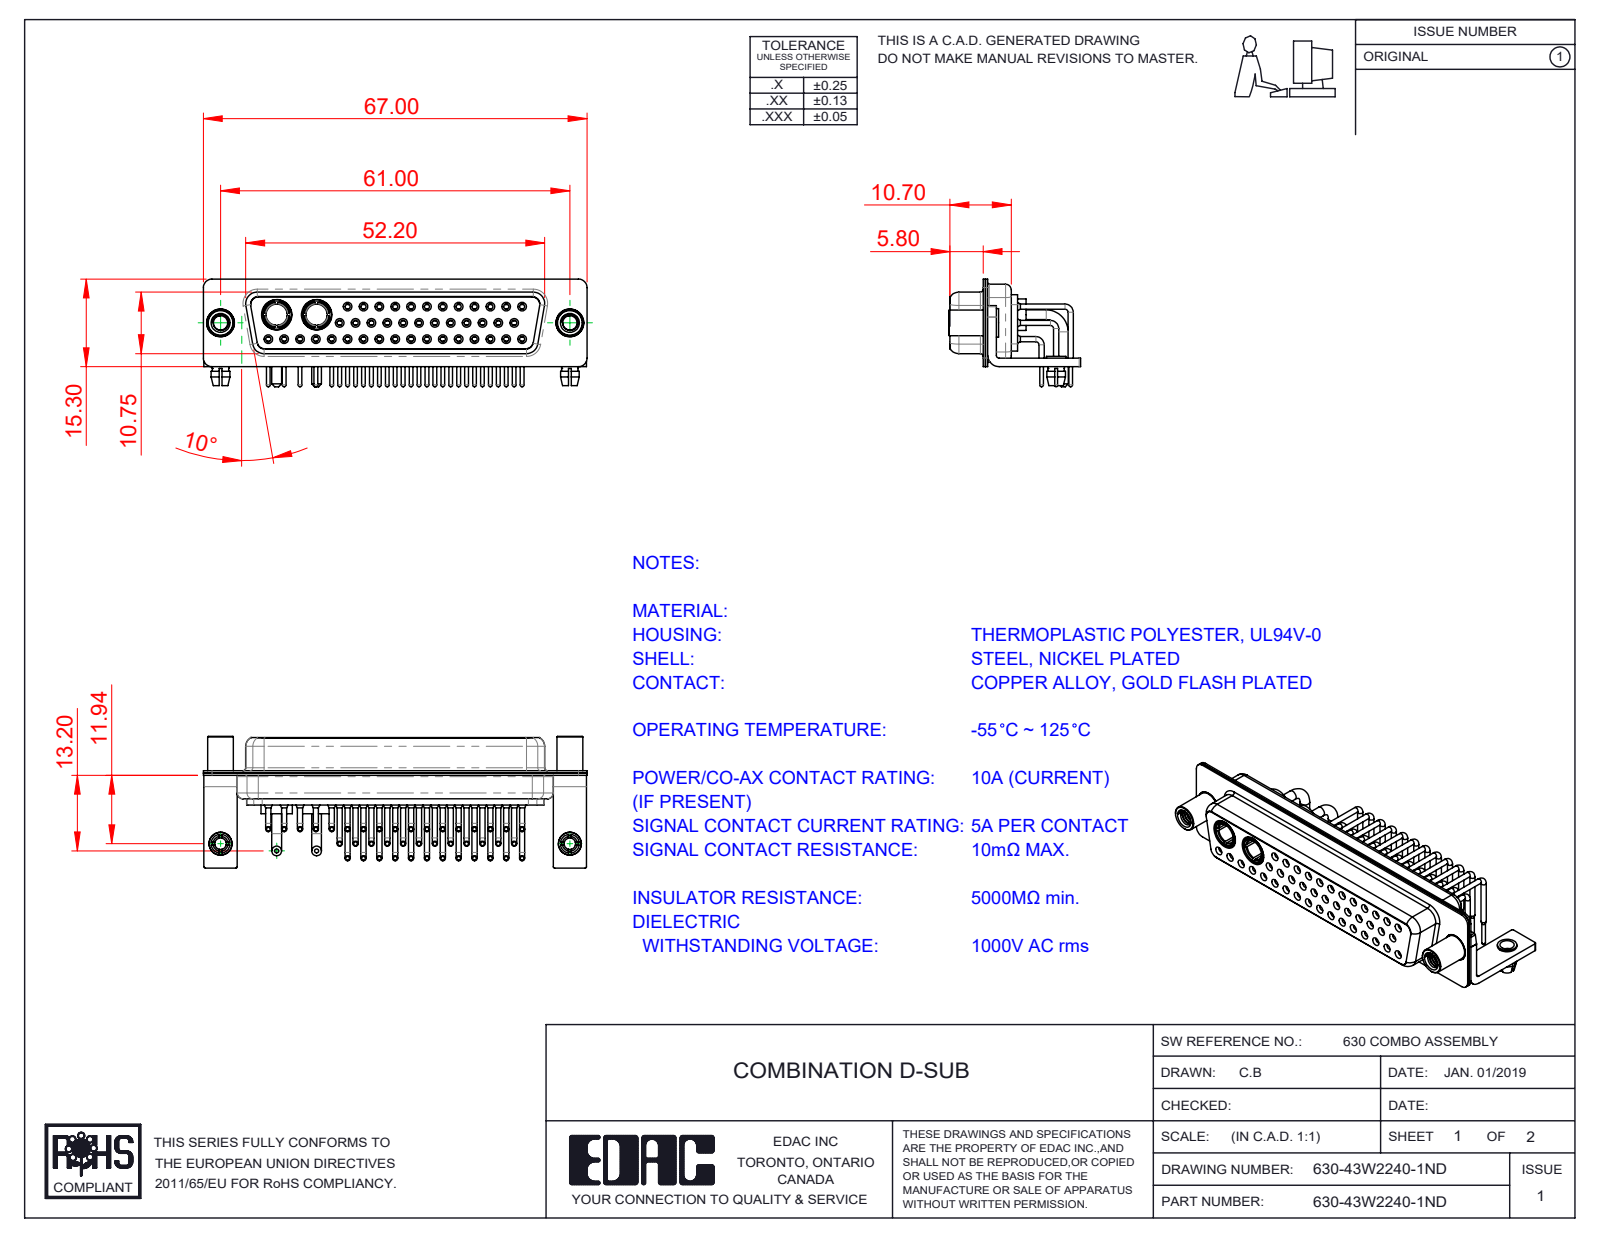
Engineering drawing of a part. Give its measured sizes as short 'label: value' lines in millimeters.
name: 630-43W2240-1ND; 630Combo Contact Row 2_50 Contacts; 630Combo Shell Front_50 Contacts; 630Combo Shell Rear_50 Contacts (+7 more)
written by: SolidWorks 2020 (CONFIG_CONTROL_DESIGN)
unit: mm
bodies: 54 solids, 2798 faces (810 planar, 1234 cylindrical, 754 other)
size: 67 × 23 × 18.8
volume: 7 582 mm³; area: 16 992 mm²
holes: 43× ⌀2, 41× ⌀0.9, 41× ⌀1.1, 41× ⌀1.5, 29× ⌀1.6, 12× ⌀1.7, 4× ⌀2.5, 4× ⌀4.85, 2× ⌀3.2, 2× ⌀3.7, 2× ⌀4, 2× ⌀4.05
bosses: 41× ⌀0.9, 41× ⌀0.65, 12× ⌀1.6, 4× ⌀1.7, 2× ⌀5.5, 2× ⌀5.2, 2× ⌀5, 2× ⌀4.96
rounds: 16× R0.25, 16× R1.5, 13× R2, 12× R1.35, 8× R1.6, 5× R0.5, 4× R0.6, 4× R0.65
face distances: 0.4, 1.5, 6, 5.6, 0.8, 5.2, 5.8, 11.28, 1.82, 6.2
hole spacings: 2.77, 3.16, 5.54, 8.31, 11.08, 13.85, 16.62, 19.39
